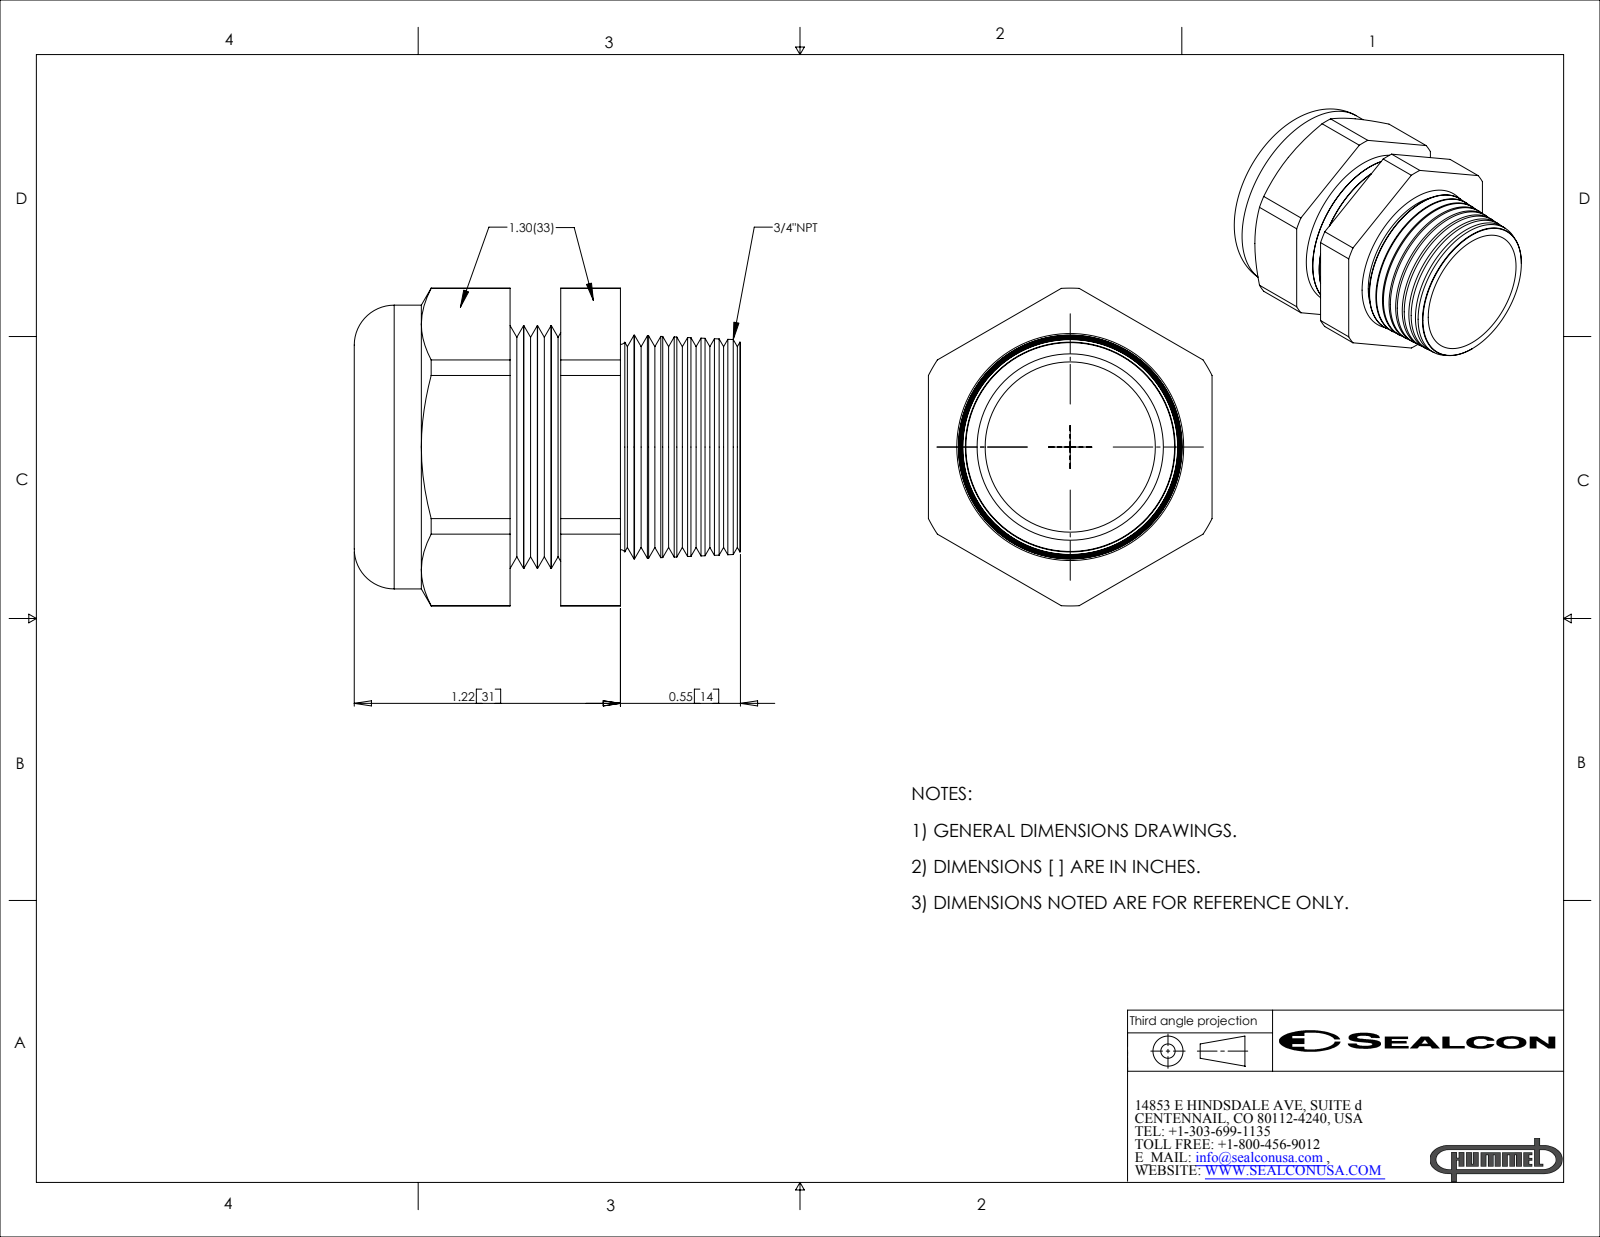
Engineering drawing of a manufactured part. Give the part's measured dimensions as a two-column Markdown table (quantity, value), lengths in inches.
| quantity | value |
| --- | --- |
| part name | CD21NA-GY |
| STEP written by | SolidWorks 2007 (CONFIG_CONTROL_DESIGN) |
| units | inches |
| bodies | 2 solids, 136 faces (20 planar, 30 cylindrical, 86 other) |
| overall size | 1.77 × 1.456 × 1.3 |
| volume | 1.079 in³ |
| surface area | 17.78 in² |
| round holes (diameter × count) | 0.78 × 1, 0.876 × 1 |
| round bosses / shafts (diameter × count) | 1.3 × 1, 1.113 × 1 |
| partial cylindrical surfaces (radius × count) | 0.728 × 1 |
| main face-to-face distances | 1.3, 0.506, 0.232, 0.274, 0.407, 0.639, 0.913, 1.463, 1.056, 0.824 |
